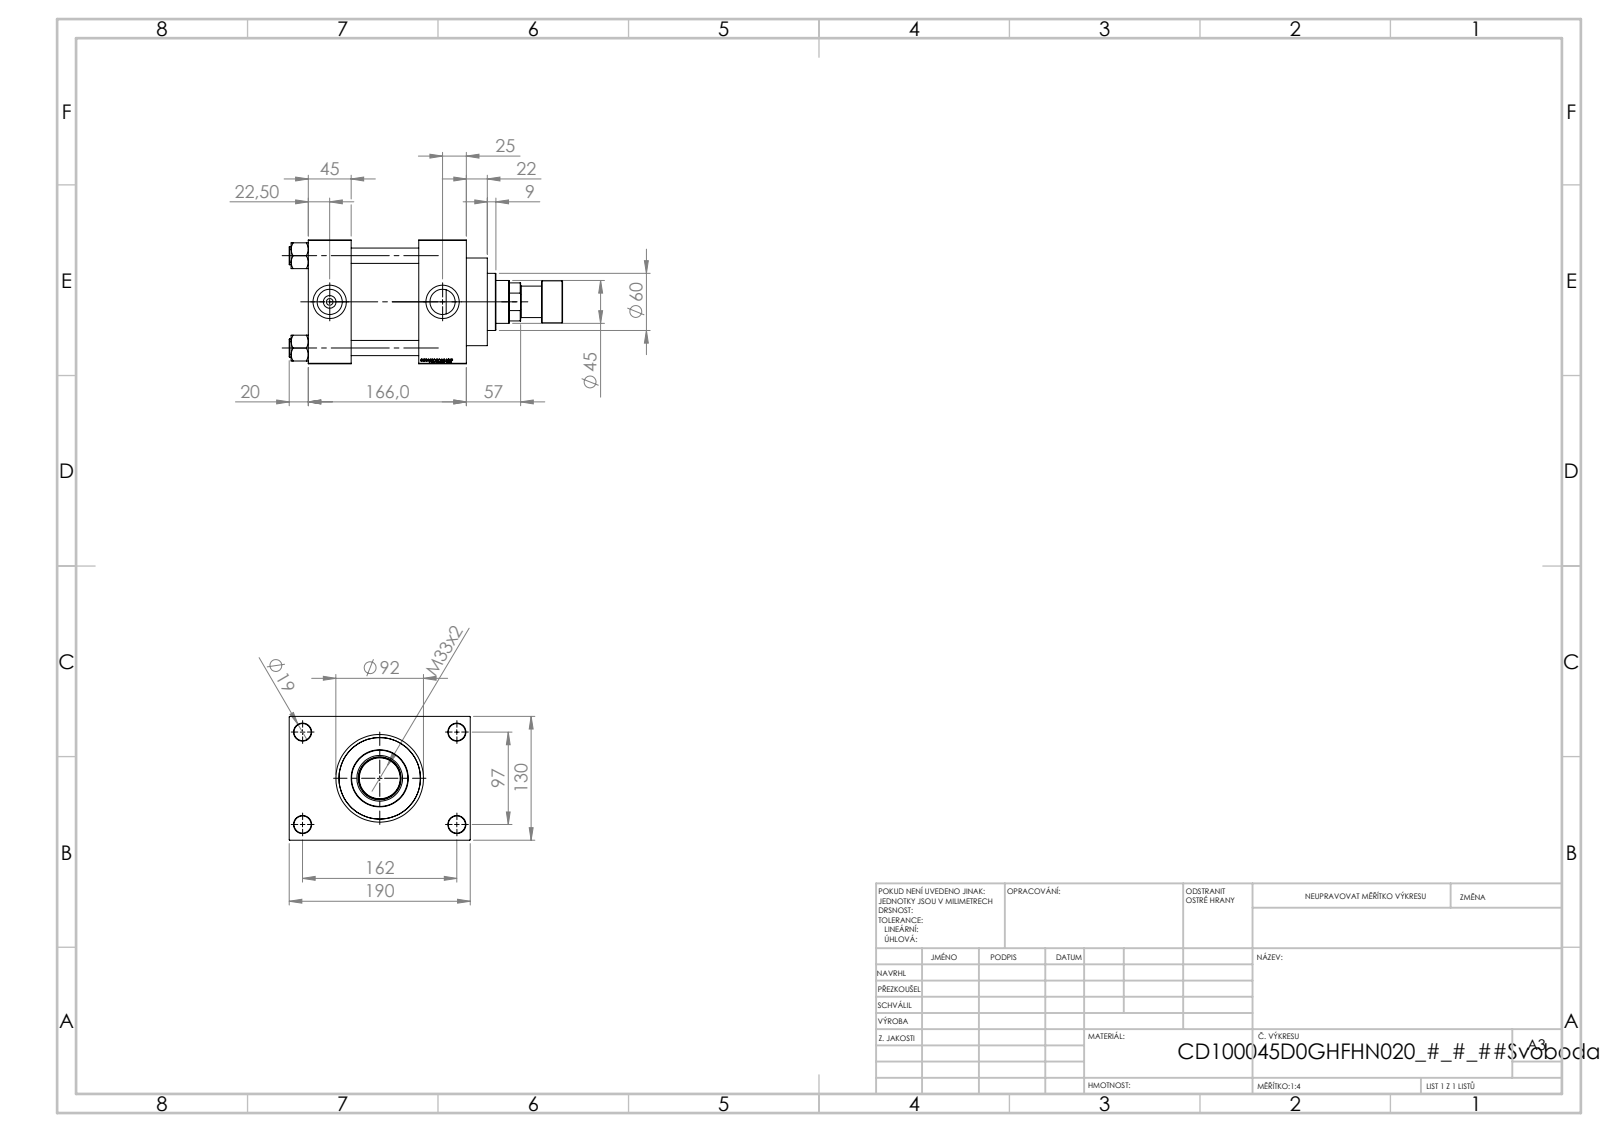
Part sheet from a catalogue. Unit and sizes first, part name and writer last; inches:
Units: inches
Overall size (bounding box): 11.299 × 7.48 × 5.118
Round holes (diameter × count): ⌀0.63 ×4, ⌀0.709 ×4, ⌀0.276 ×2, ⌀1.041 ×2, ⌀1.378 ×2, ⌀1.24 ×1, ⌀1.772 ×1, ⌀1.89 ×1, ⌀2.992 ×1, ⌀3.366 ×1, ⌀3.937 ×1
Round bosses / shafts (diameter × count): ⌀0.748 ×4, ⌀4.173 ×1, ⌀3.622 ×1, ⌀2.362 ×1, ⌀1.732 ×1, ⌀1.299 ×1
Main face-to-face distances: 5.118, 4.567, 1.772, 2.795, 6.535, 4.764, 1.969, 1.181, 6.299, 2.756
Hole centre spacings: 1.281, 2.698, 3.717, 3.815, 4.026, 5.096, 6.367, 3.819
Volume: 161.3 in³ · Surface area: 563 in²
Bodies: 12 solids, 1164 faces (548 planar, 92 cylindrical, 524 other)
Part name (STEP PRODUCT): V215CD_NUT_M5_D; V215CD_VC_A; V215CD_VCP_D; V215CD_D_Body (+2 more)
STEP written by: SolidWorks 2019 (CONFIG_CONTROL_DESIGN)
